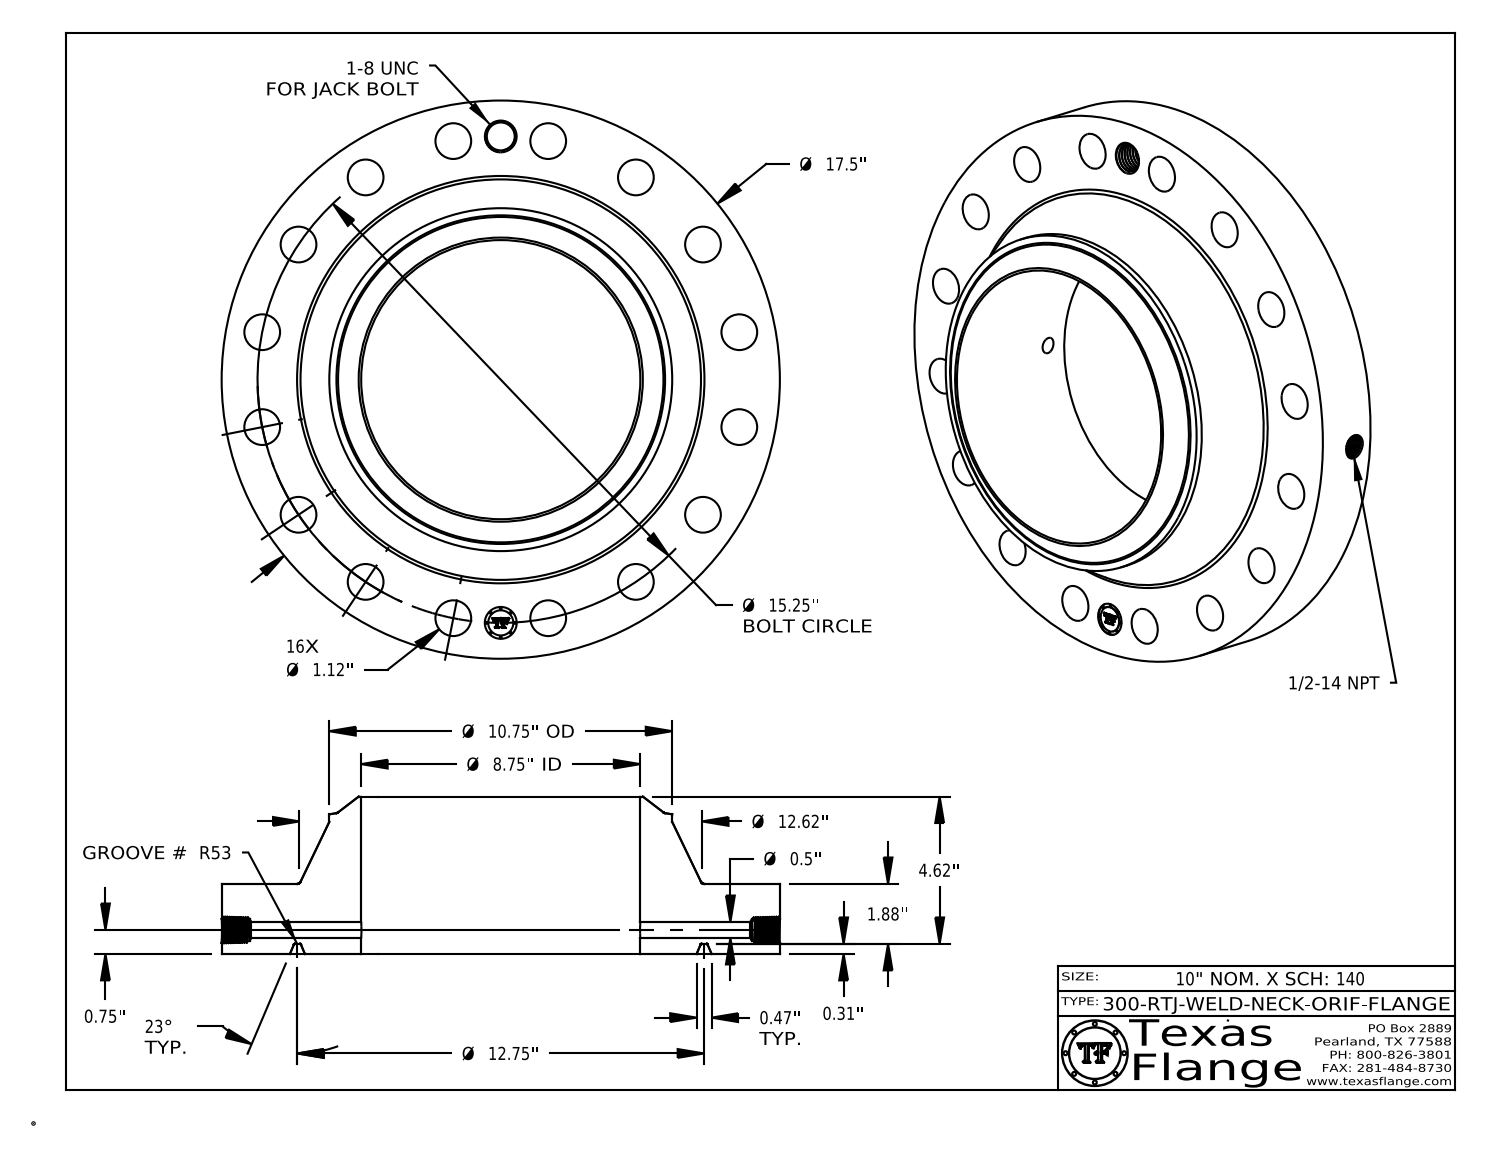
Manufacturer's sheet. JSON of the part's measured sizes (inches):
{"part_name": "300-RTJ-WELD-NECK", "step_written_by": "CATIA V5 STEP AP214 (AUTOMOTIVE_DESIGN)", "units": "inches", "bodies": {"solids": 1, "faces": 813, "planar": 370, "cylindrical": 112, "other": 331}, "overall_size": [17.5, 17.5, 4.933], "volume_in3": 459.9, "surface_area_in2": 807.7, "round_holes": [[1.12, 16], [0.5, 1], [0.672, 1], [0.875, 1], [1, 1], [8.75, 1]], "round_bosses_or_shafts": [[0.061, 8], [17.5, 1], [10.75, 1], [0.788, 1]], "face_to_face_distances": [2.193, 0.313, 1.88, 4.933, 4.62, 2.74, 0.015, 2.178, 1.865, 2.755], "hole_center_spacings": [5.836, 7.625, 10.783, 14.089, 14.957, 2.975, 2.975, 8.472]}
